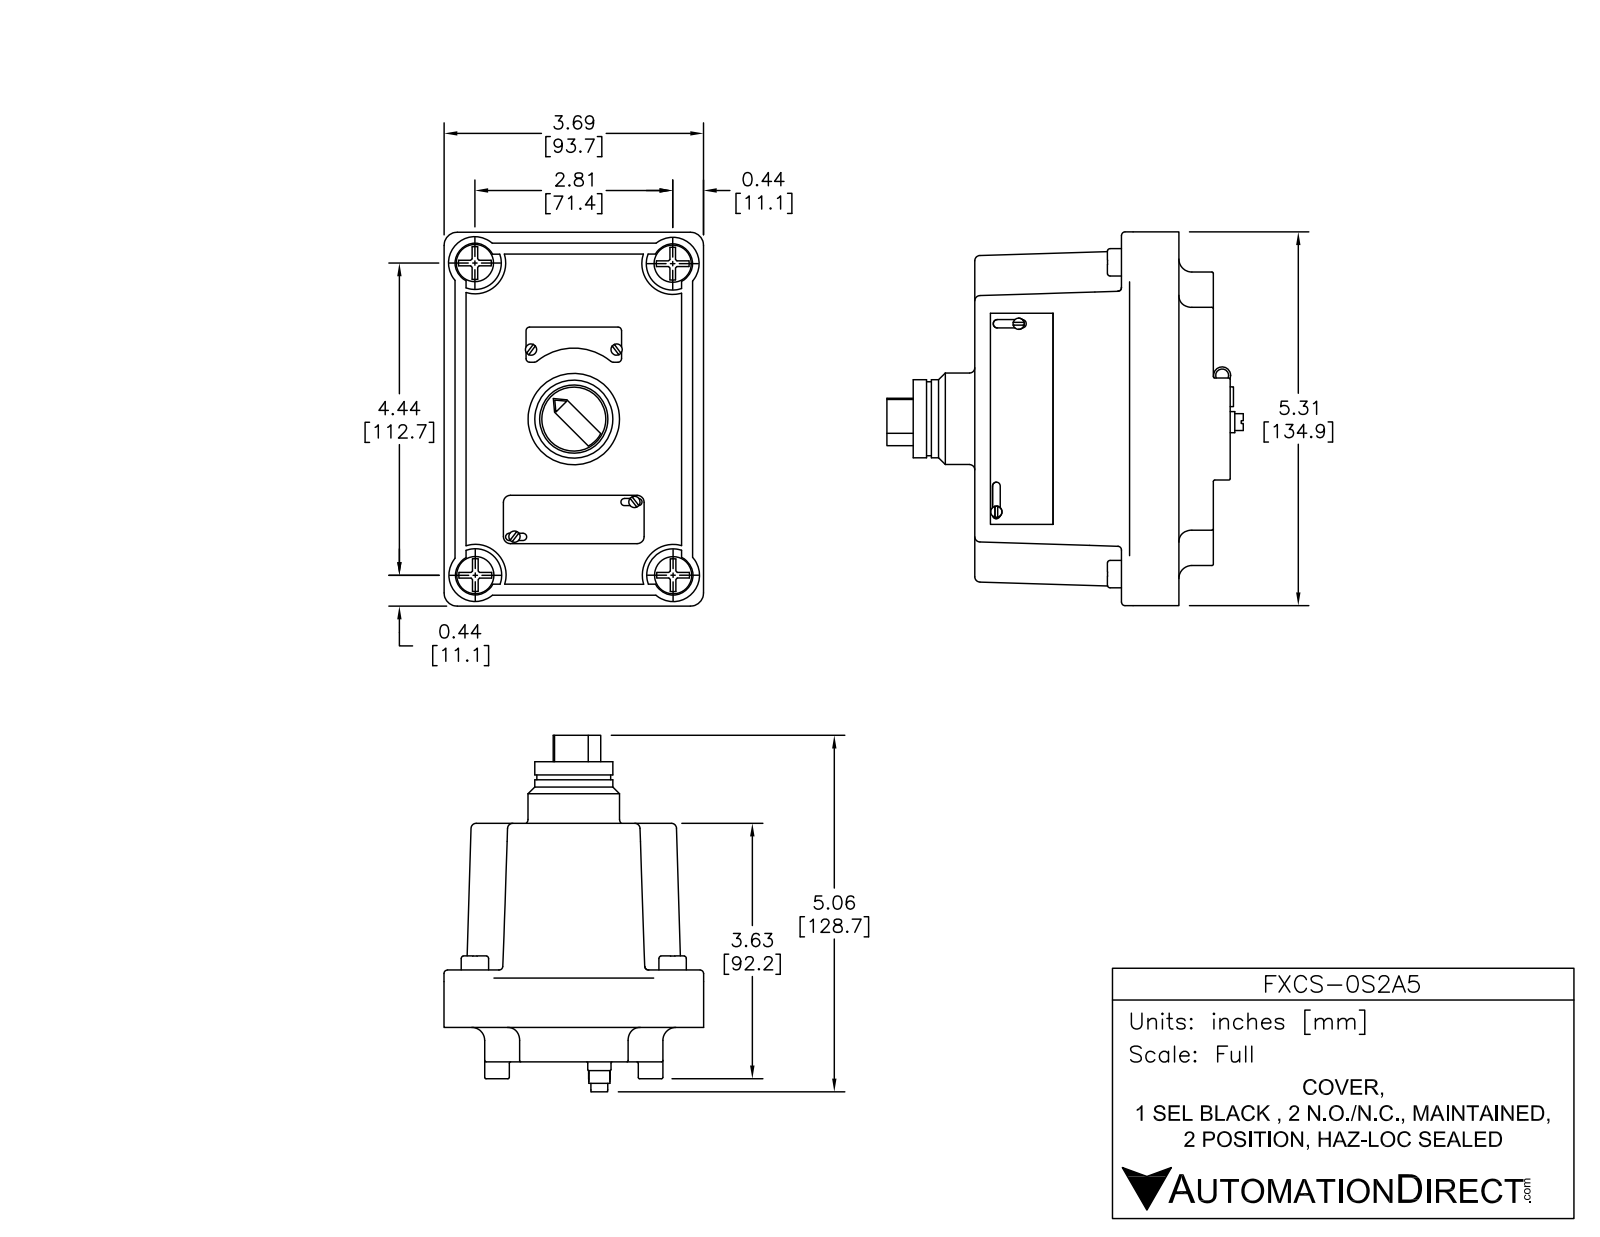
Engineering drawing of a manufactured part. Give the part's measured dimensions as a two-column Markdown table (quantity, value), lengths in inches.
| quantity | value |
| --- | --- |
| part name | FXCS-0S2A5 |
| STEP written by | SolidWorks 2015 (AUTOMOTIVE_DESIGN) |
| units | inches |
| bodies | 2 solids, 710 faces (308 planar, 166 cylindrical, 236 other) |
| overall size | 5.31 × 5.066 × 3.69 |
| volume | 48.91 in³ |
| surface area | 100.9 in² |
| round holes (diameter × count) | 0.16 × 8, 0.198 × 1, 0.97 × 1 |
| round bosses / shafts (diameter × count) | 0.16 × 8, 0.39 × 4, 1.3 × 1, 1.11 × 1, 1.05 × 1, 0.91 × 1, 0.33 × 1, 0.3 × 1 |
| partial cylindrical surfaces (radius × count) | 0.05 × 24, 0.02 × 22, 0.051 × 4, 0.055 × 4, 0.06 × 4, 0.075 × 4, 0.1 × 4, 0.185 × 4 |
| main face-to-face distances | 3.39, 0.49, 2.9, 0.021, 3.69, 0.578, 3.111, 1.19, 0.7, 2.2 |
| hole center spacings | 0.25, 2.197, 0.5, 2.183, 2.239, 0.75, 1.092, 1.115 |
